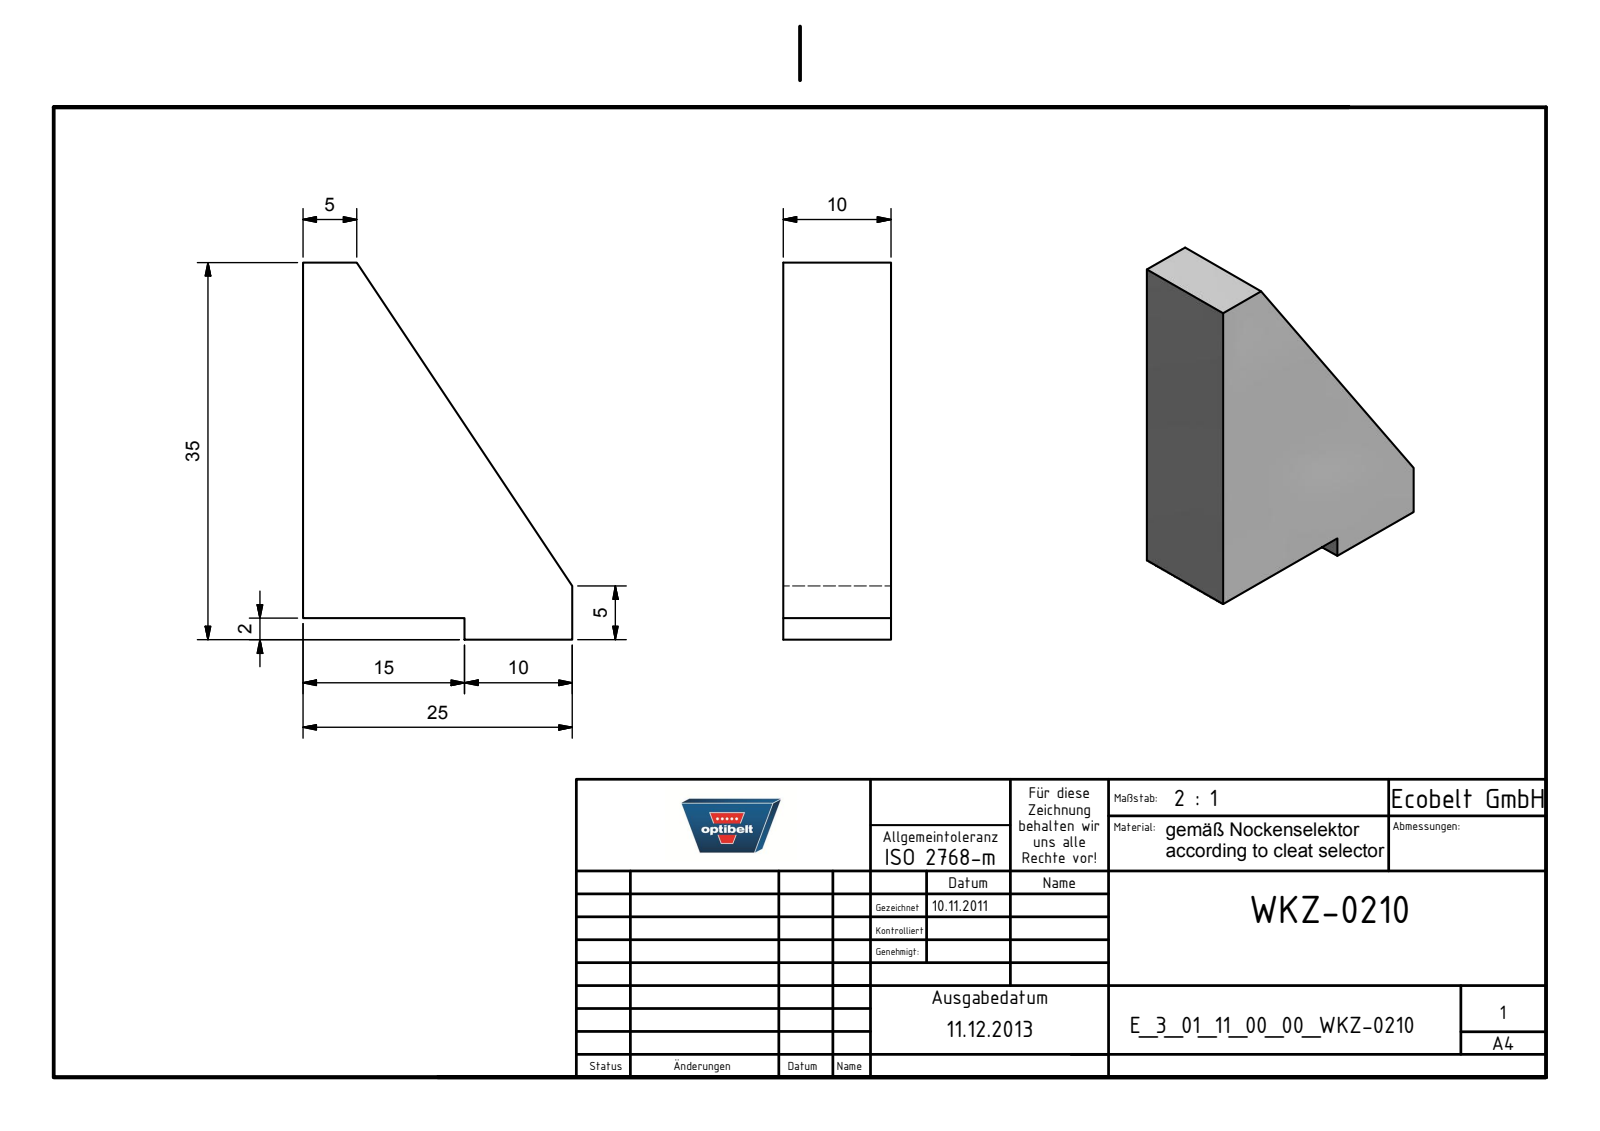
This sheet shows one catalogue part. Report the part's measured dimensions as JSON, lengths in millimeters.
{"part_name": "E_3_01_11_00_00_WKZ-0210", "step_written_by": "Autodesk Inventor 2018 (AUTOMOTIVE_DESIGN)", "units": "millimeters", "bodies": {"solids": 1, "faces": 9, "planar": 9, "cylindrical": 0, "other": 0}, "overall_size": [35, 25, 10], "volume_mm3": 5450, "surface_area_mm2": 2151, "face_to_face_distances": [10, 2, 25, 35, 33, 15]}
